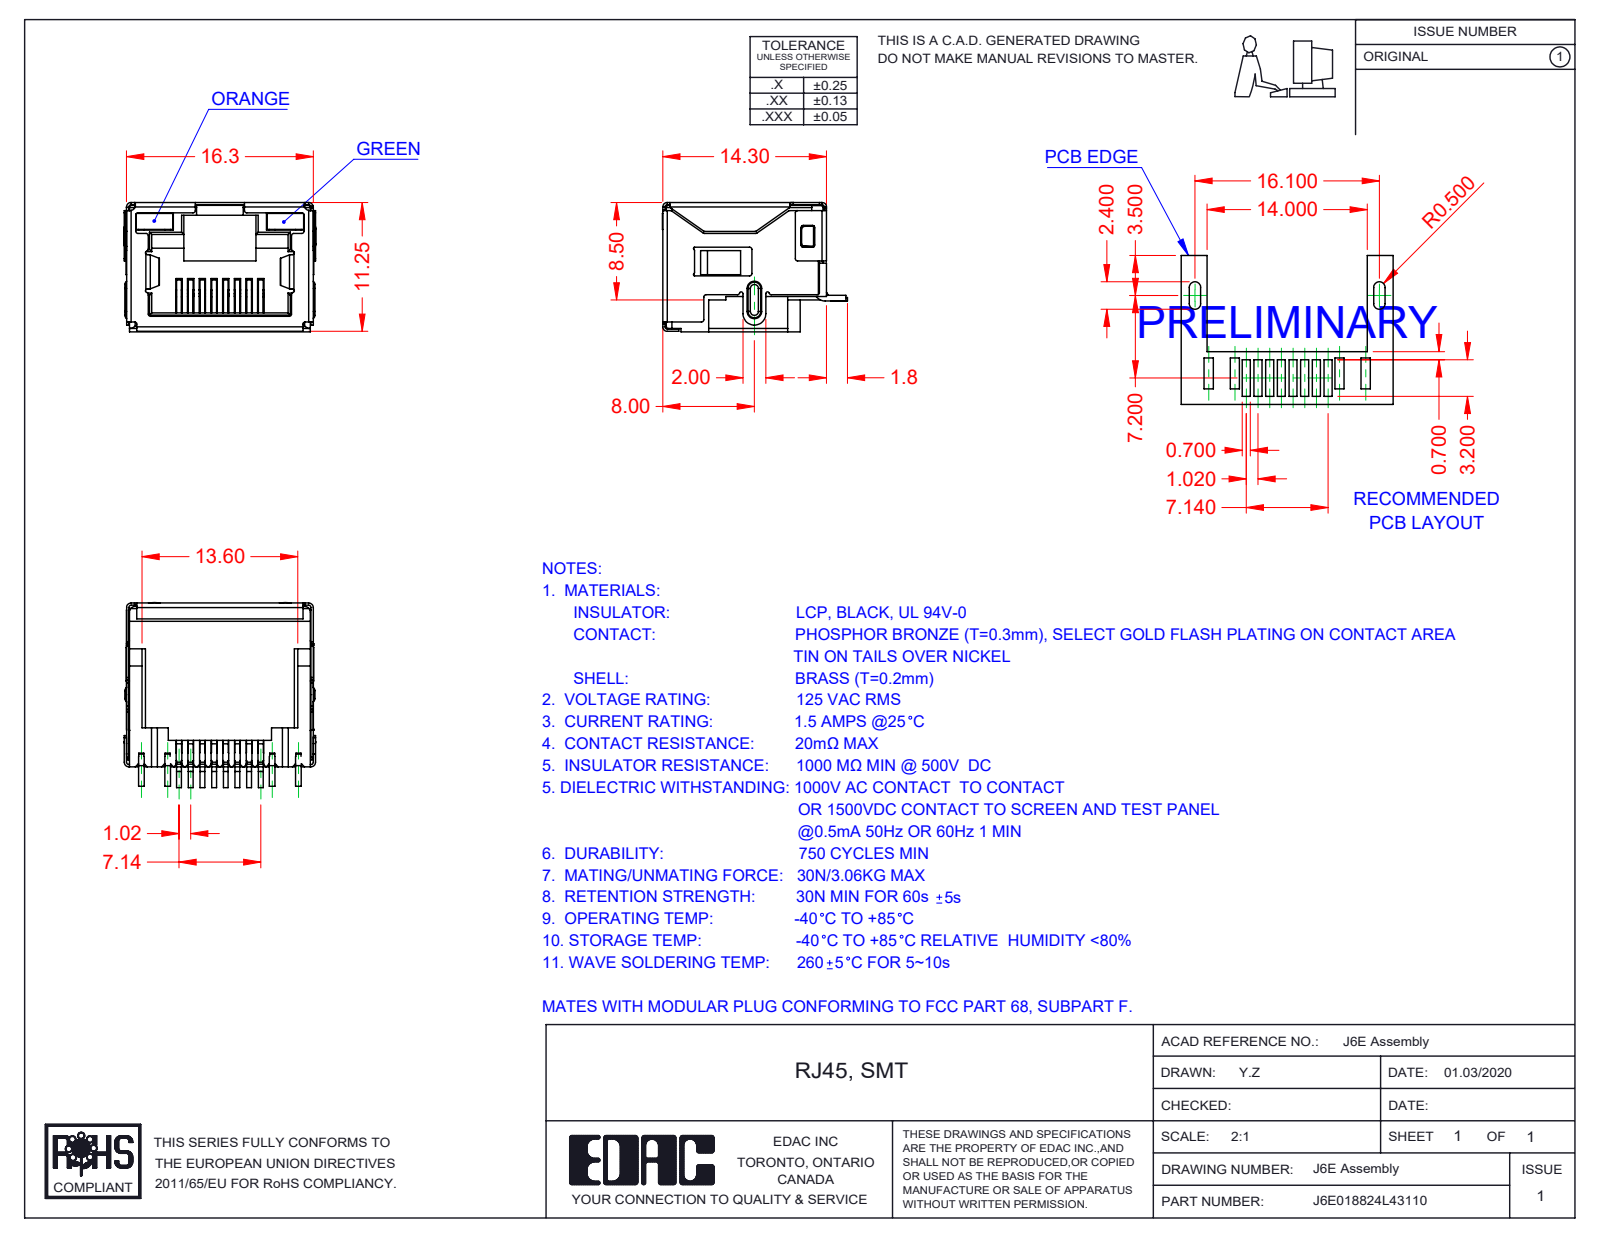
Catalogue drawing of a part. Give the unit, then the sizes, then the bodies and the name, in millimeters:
Units: millimetres
Overall size (bounding box): 16.75 × 16.15 × 11.3
Partial cylindrical surfaces — rounded edges, fillets, slot ends (radius × count): R0.2 ×82, R0.25 ×17, R0.4 ×13, R0.5 ×13, R0.1 ×10, R0.15 ×7, R0.3 ×4, R1 ×3
Main face-to-face distances: 11.05, 16.05, 16.1, 15.85, 11.1, 11.3, 2.4, 0.7, 9.85, 0.49
Volume: 1 109 mm³ · Surface area: 4 045 mm²
Bodies: 12 solids, 1496 faces (1099 planar, 347 cylindrical, 50 other)
Part name (STEP PRODUCT): 6E Shield_LED; 6E Contacts; 6E Insulator_LED; J6E018824L43110 (+2 more)
STEP written by: SolidWorks 2016 (CONFIG_CONTROL_DESIGN)
